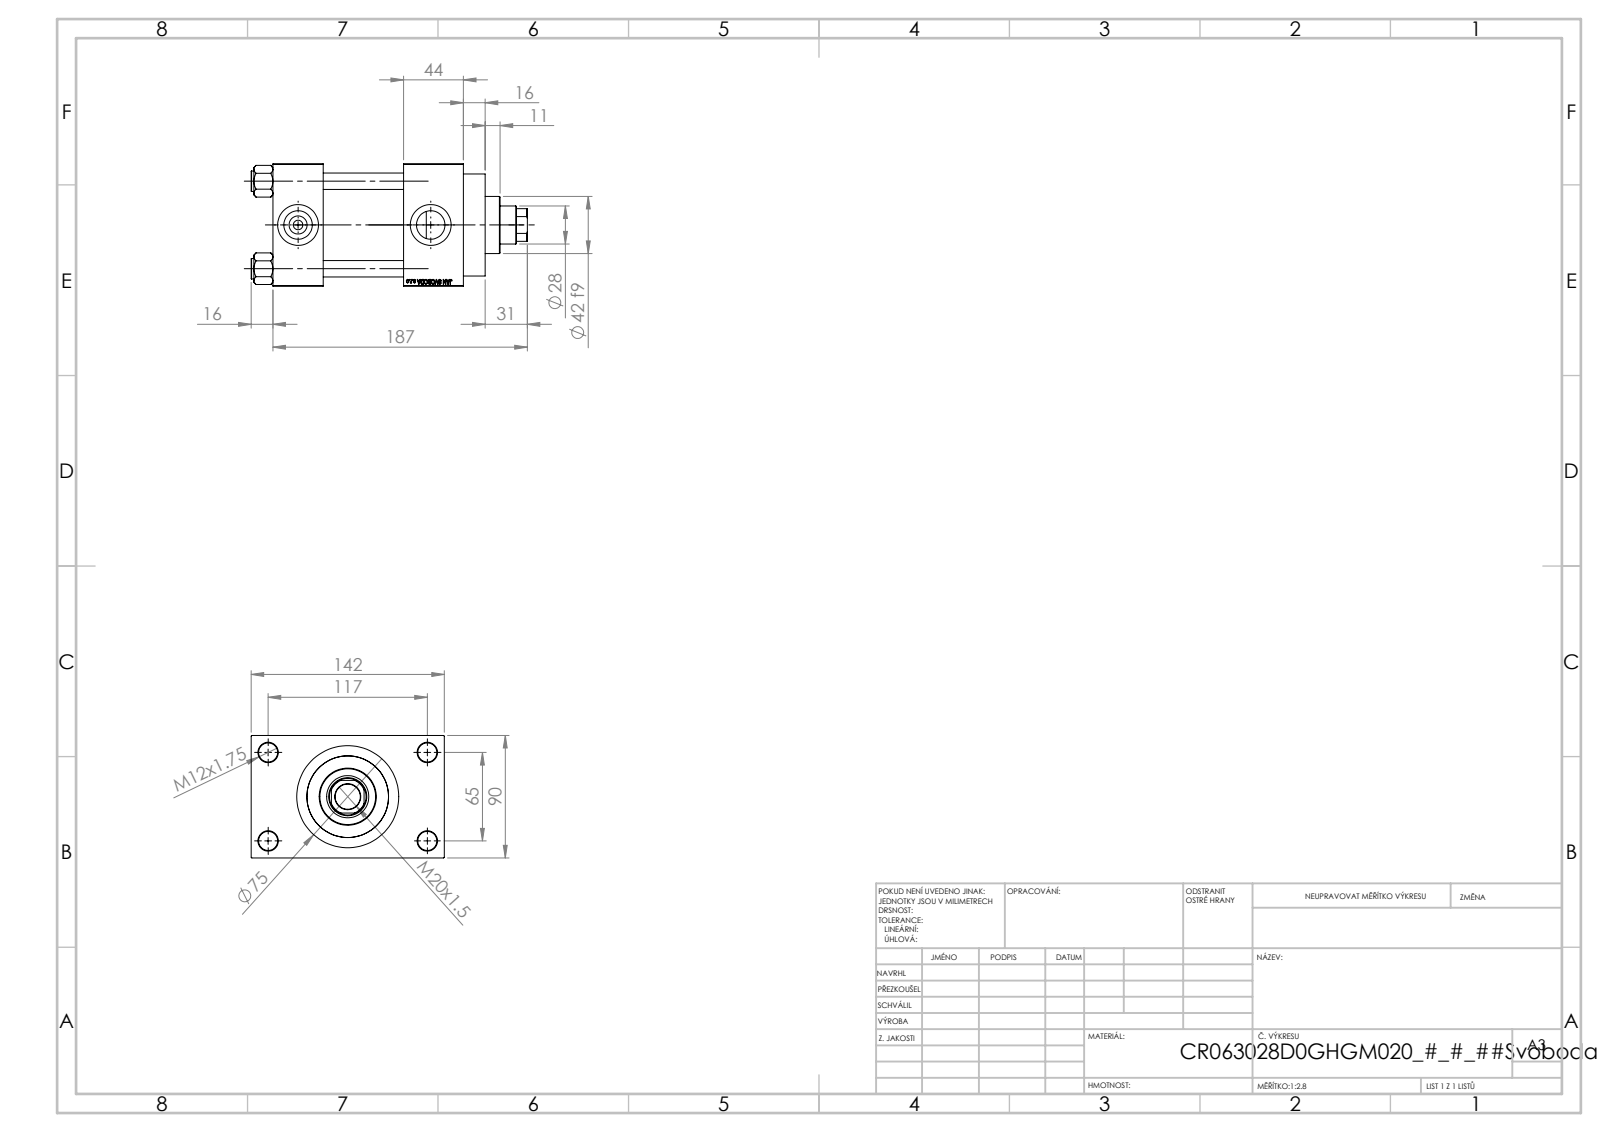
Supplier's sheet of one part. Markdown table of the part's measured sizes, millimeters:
| quantity | value |
| --- | --- |
| part name | V215CR_D_TYCINKA; V215CR_VCP_D; NUT_M5_D; V215CR_D_Body (+1 more) |
| STEP written by | SolidWorks 2019 (CONFIG_CONTROL_DESIGN) |
| units | millimeters |
| bodies | 11 solids, 1103 faces (497 planar, 88 cylindrical, 518 other) |
| overall size | 203 × 142 × 90 |
| volume | 1 096 000 mm³ |
| surface area | 200 314 mm² |
| round holes (diameter × count) | 12 × 4, 14 × 4, 7 × 2, 20.96 × 2, 30 × 2, 18.5 × 1, 28 × 1, 31 × 1, 50 × 1, 60 × 1, 63 × 1 |
| round bosses / shafts (diameter × count) | 15 × 4, 75 × 1, 69 × 1, 42 × 1 |
| partial cylindrical surfaces (radius × count) | 13.5 × 1 |
| main face-to-face distances | 90, 59, 37, 96, 140, 103, 44, 26, 116, 16 |
| hole center spacings | 26.35, 45.47, 64.3, 66.92, 69.81, 90.65, 111.34, 65 |
